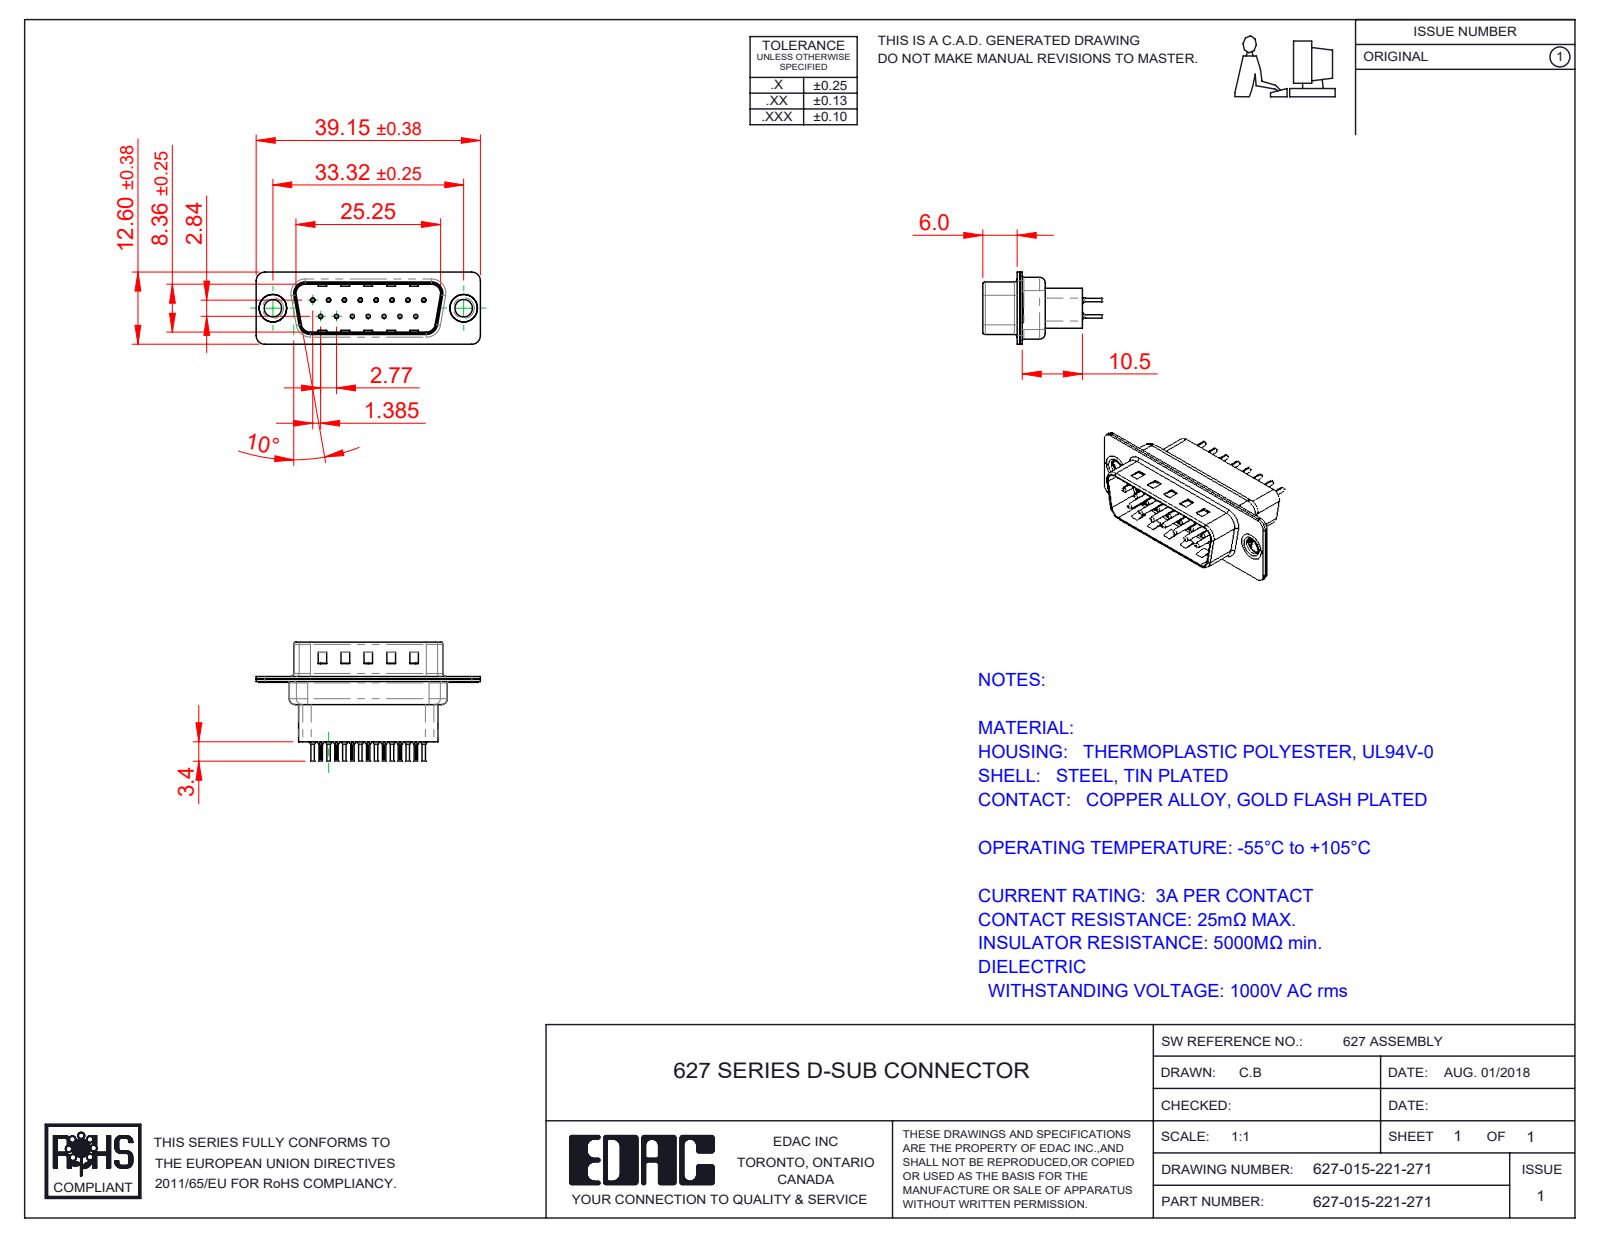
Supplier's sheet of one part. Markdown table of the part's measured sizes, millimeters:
| quantity | value |
| --- | --- |
| part name | 627-015-221-071; 627 Thru Hole Rivet; 627 Contact Row 2_21H; 627 Shell Front_15 Contacts (+3 more) |
| STEP written by | SolidWorks 2020 (CONFIG_CONTROL_DESIGN) |
| units | millimeters |
| bodies | 20 solids, 1784 faces (499 planar, 672 cylindrical, 613 other) |
| overall size | 39.15 × 20.8 × 12.6 |
| volume | 2 461 mm³ |
| surface area | 6 466 mm² |
| round holes (diameter × count) | 0.2 × 15, 0.35 × 15, 1.1 × 15, 1.6 × 15, 3.05 × 2, 4 × 2, 4.8 × 2 |
| round bosses / shafts (diameter × count) | 2 × 15, 1.5 × 15, 0.75 × 15, 0.6 × 15, 5 × 2, 4.9 × 2, 3.55 × 2 |
| partial cylindrical surfaces (radius × count) | 0.1 × 30, 1.5 × 16, 2 × 12, 0.5 × 8, 1.6 × 8, 0.25 × 4, 0.6 × 4, 0.65 × 4 |
| main face-to-face distances | 0.4, 0.45, 0.9, 0.82, 9.58, 1.5, 0.68, 7.68, 1.4, 1.08 |
| hole center spacings | 3.16, 2.77, 5.54, 8.31, 11.08, 5.03, 5.04, 7.48 |
